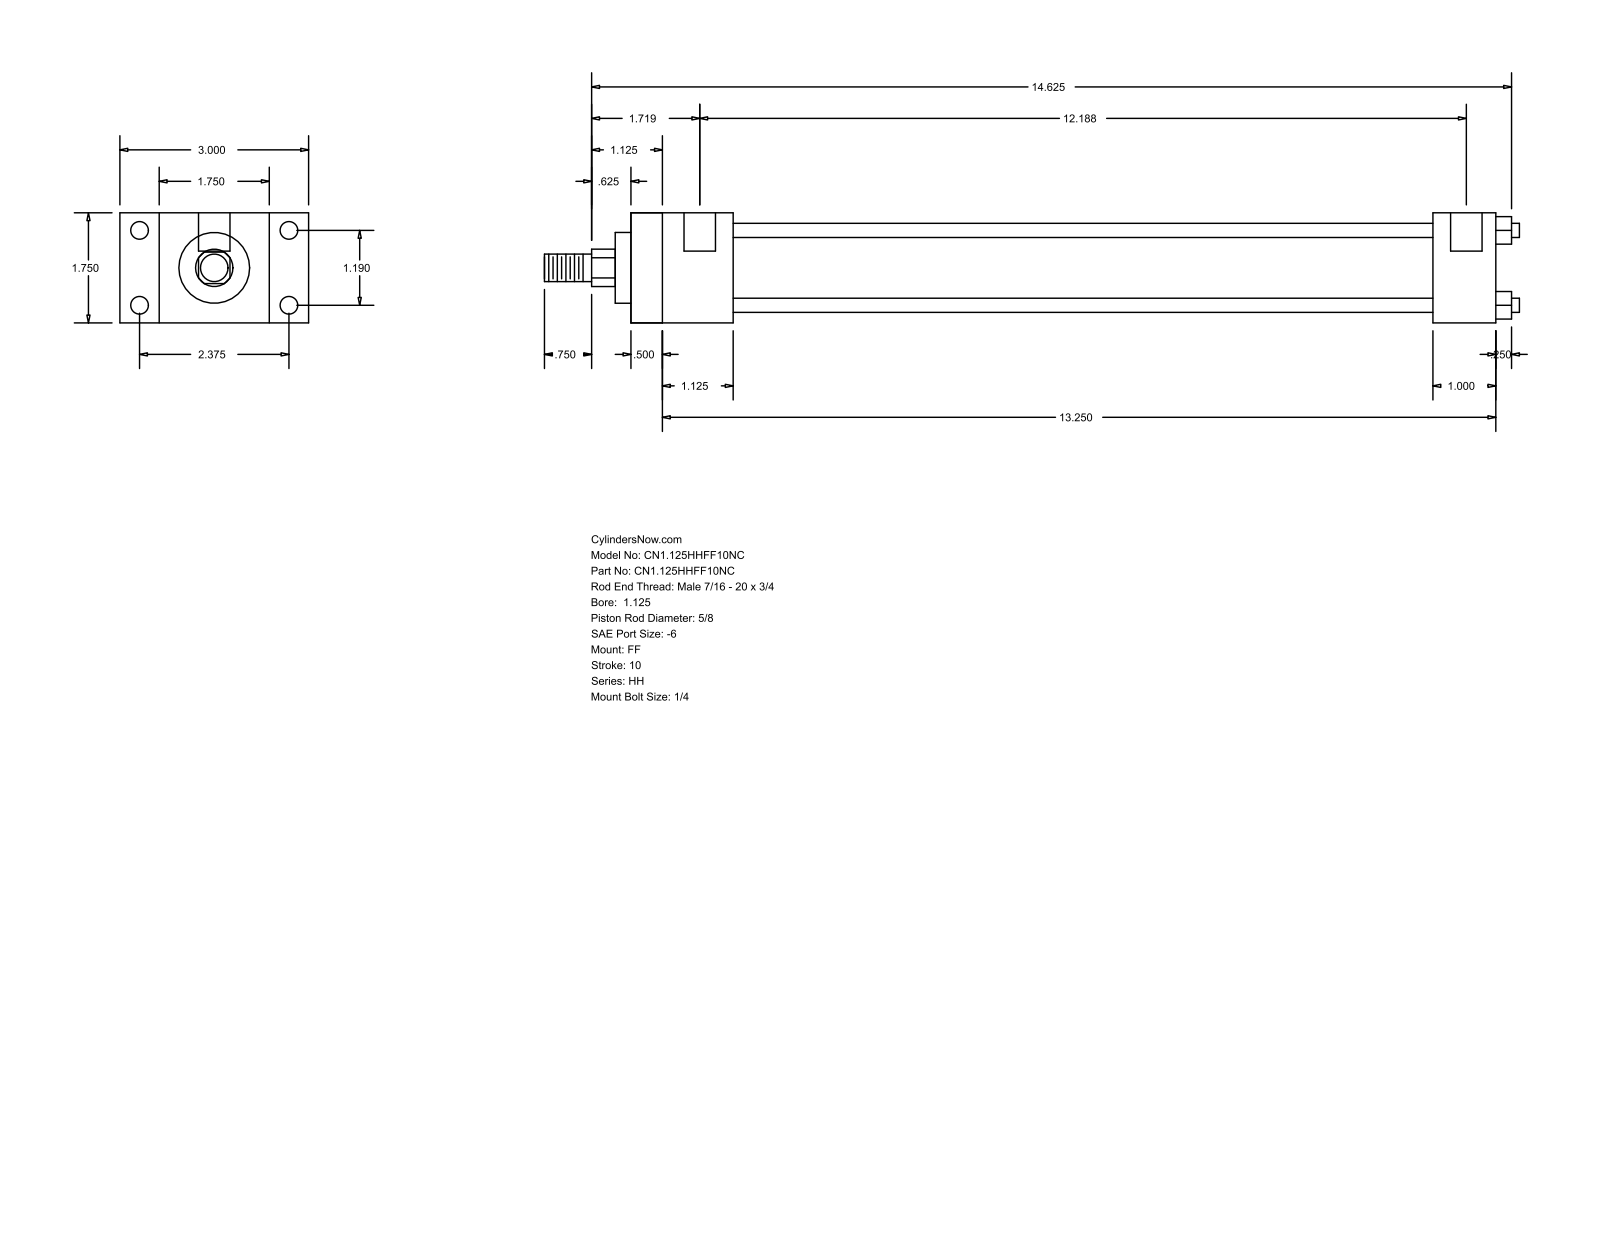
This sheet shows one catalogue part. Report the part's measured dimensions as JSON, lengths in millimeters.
{"part_name": "HH_FF__0112_0.625", "step_written_by": "GSSL Pune (CONFIG_CONTROL_DESIGN)", "units": "millimeters", "bodies": {"solids": 0, "faces": 92, "planar": 64, "cylindrical": 28, "other": 0}, "overall_size": [393.7, 76.2, 44.45], "round_holes": [[5.56, 4], [7.14, 4], [12.7, 2]], "round_bosses_or_shafts": [[5.71, 4], [34.92, 1], [28.57, 1], [15.88, 1], [11.11, 1]], "partial_cylinders_radius": [[7.54, 1]], "face_to_face_distances": [44.46, 349.24, 15.87, 12.69, 336.55, 28.58, 60.33, 41.27, 323.85, 311.16], "hole_center_spacings": [30.22, 60.32, 67.47, 306.39, 3.17, 309.56]}
